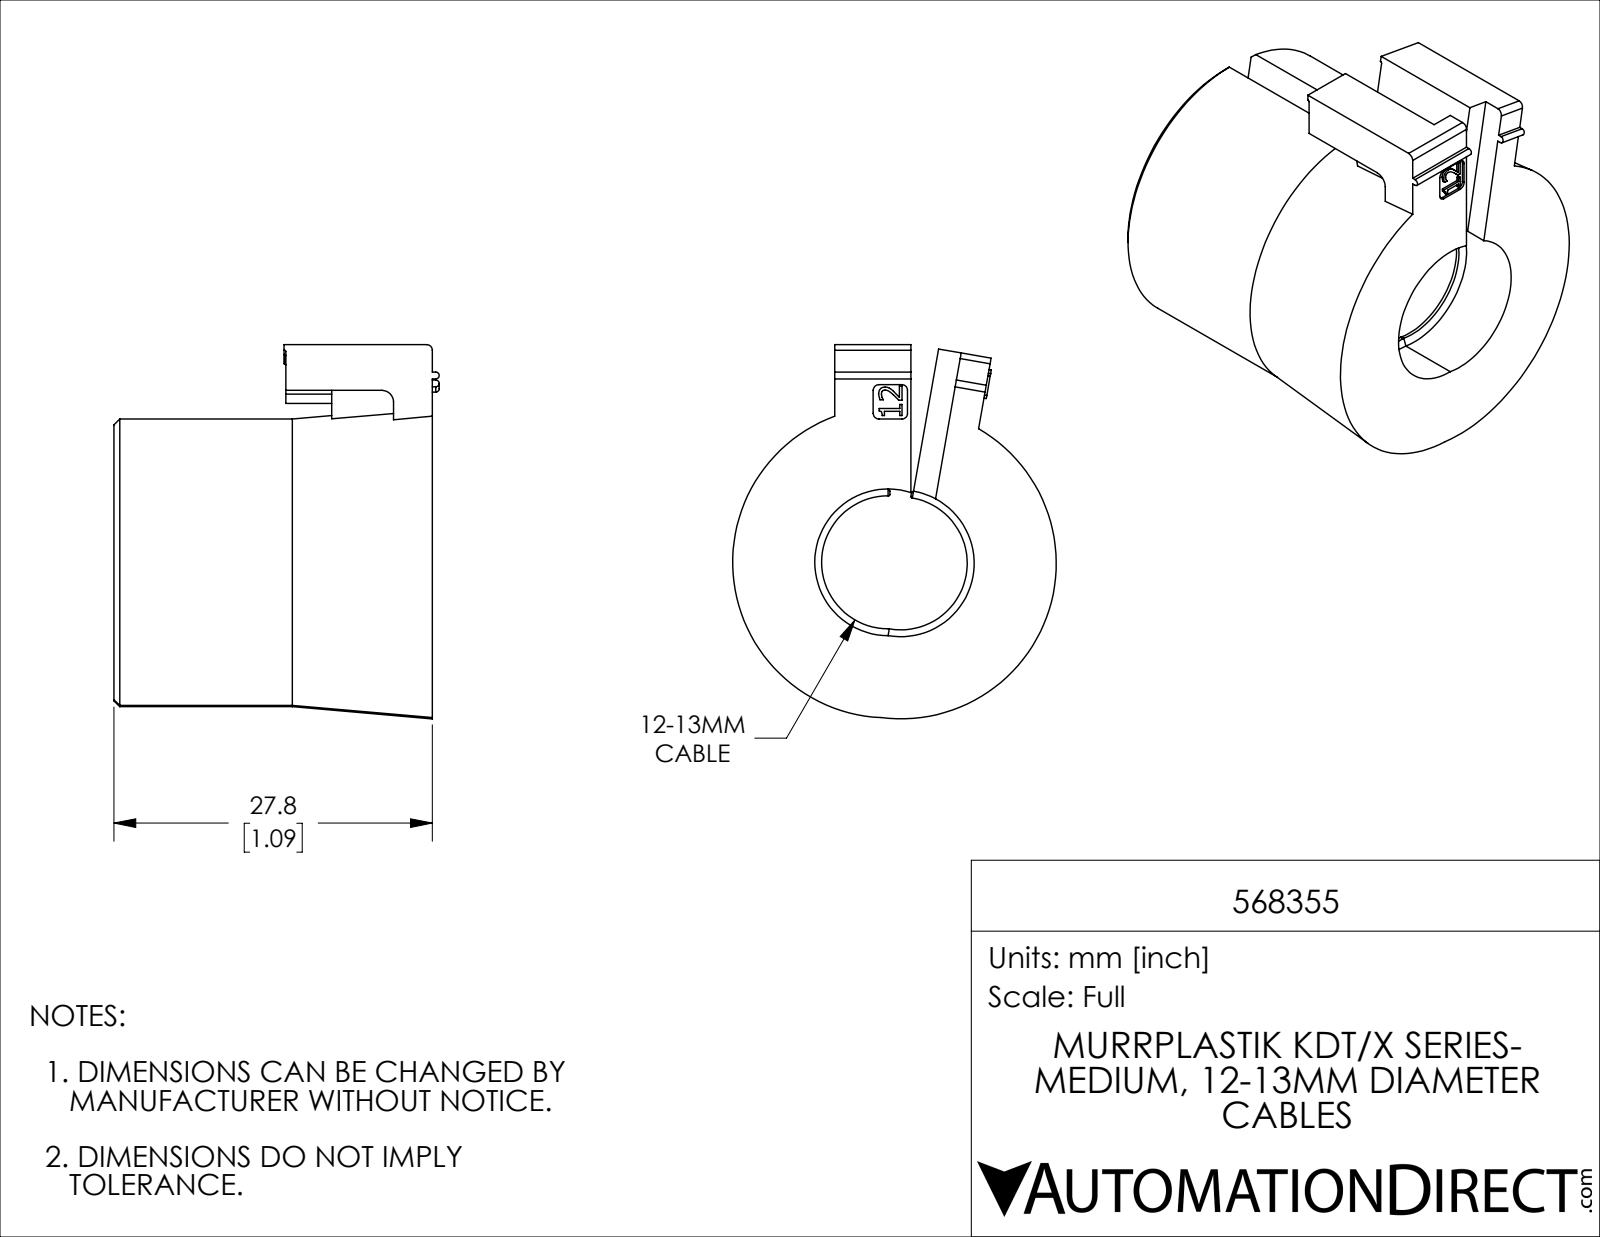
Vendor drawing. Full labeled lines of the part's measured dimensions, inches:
Part name (STEP PRODUCT): 568355
STEP written by: SolidWorks 2019 (CONFIG_CONTROL_DESIGN)
Units: inches
Bodies: 1 solid, 131 faces (77 planar, 29 cylindrical, 25 other)
Overall size (bounding box): 1.286 × 1.118 × 1.112
Volume: 0.678 in³ · Surface area: 7.816 in²
Partial cylindrical surfaces — rounded edges, fillets, slot ends (radius × count): R0.004 ×6, R0.02 ×6, R0.012 ×2, R0.039 ×2, R0.228 ×2, R0.252 ×2, R0.492 ×2
Main face-to-face distances: 1.094, 0.079, 0.157, 0.183, 0.183, 1.016, 0.425, 0.504, 0.591, 0.104
